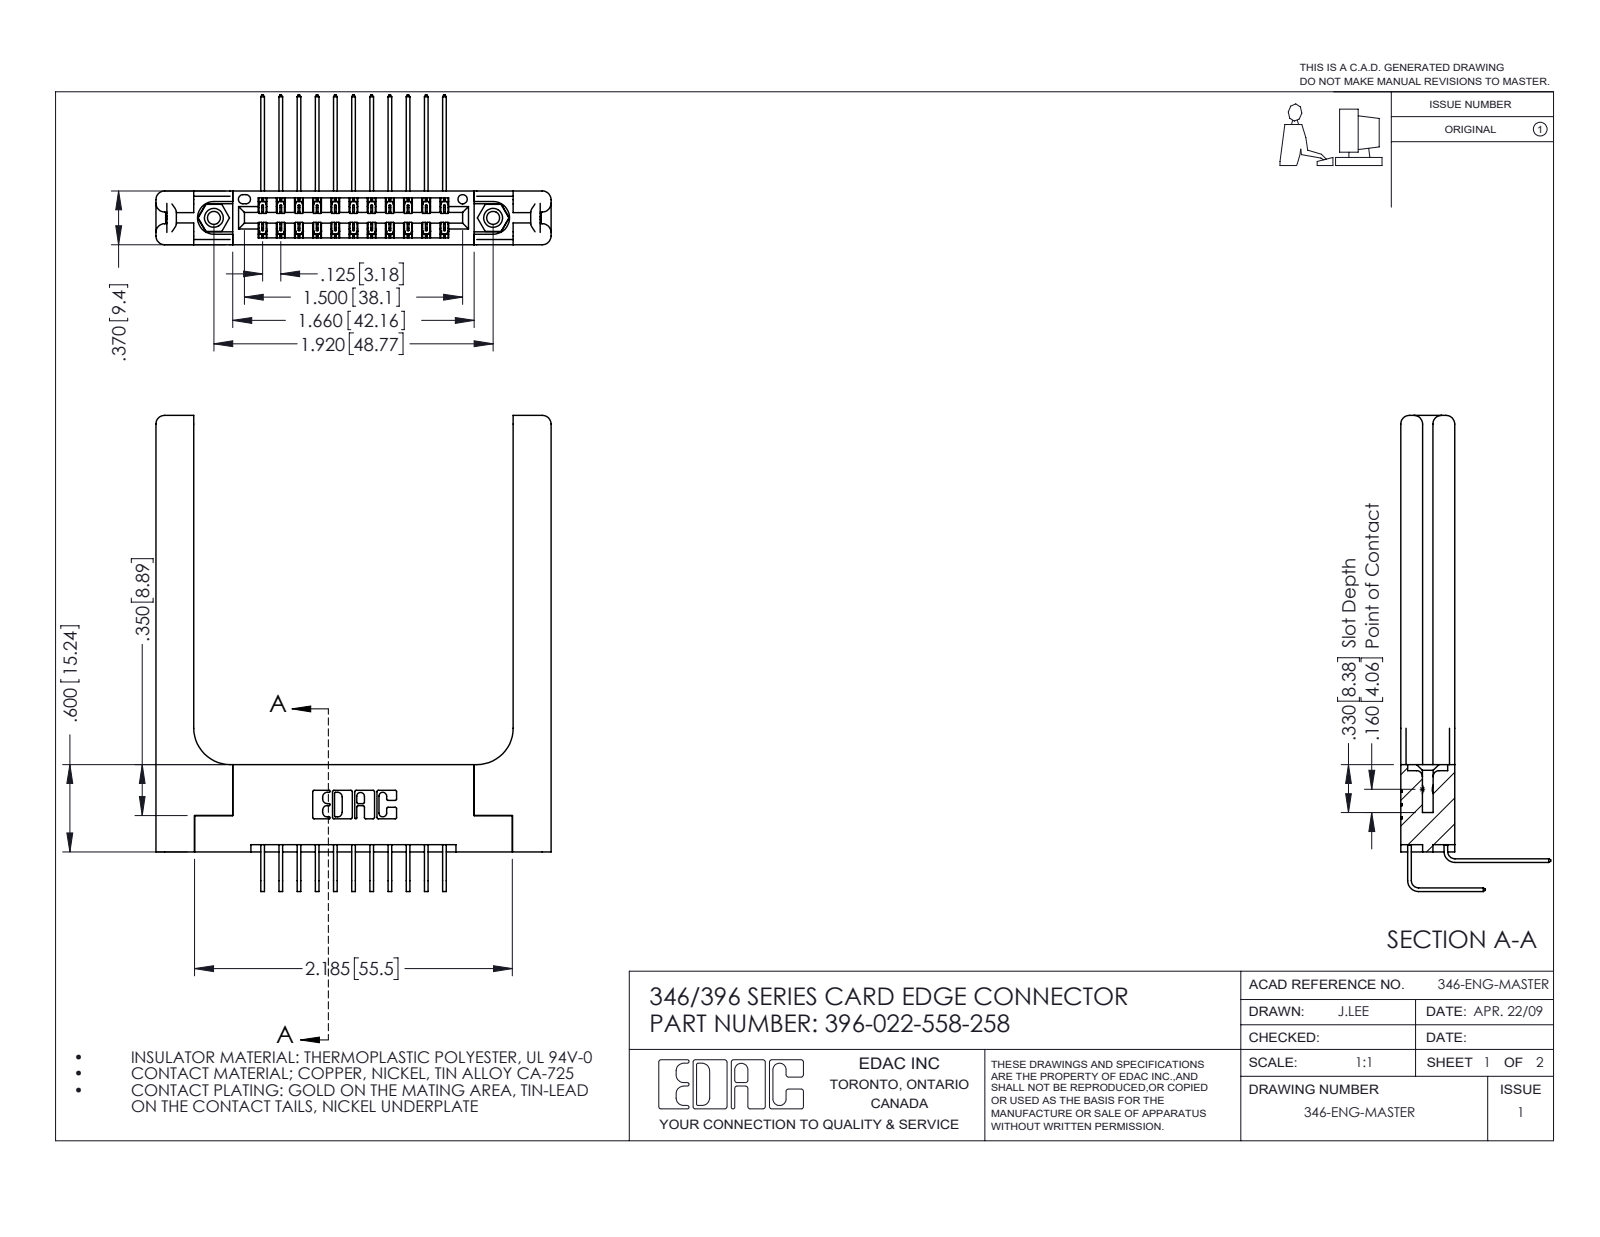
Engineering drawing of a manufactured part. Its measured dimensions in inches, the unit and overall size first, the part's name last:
Units: inches
Overall size (bounding box): 3.273 × 2.716 × 1.03
Round holes (diameter × count): ⌀0.089 ×2, ⌀0.125 ×2, ⌀0.156 ×2, ⌀0.064 ×1
Round bosses / shafts (diameter × count): ⌀0.155 ×2
Partial cylindrical surfaces — rounded edges, fillets, slot ends (radius × count): R0.006 ×33, R0.01 ×22, R0.06 ×16, R0.007 ×6, R0.031 ×6, R0.026 ×3, R0.014 ×2, R0.022 ×2
Main face-to-face distances: 0.37, 0.15, 0.072, 0.322, 0.048, 0.148, 0.22, 0.102, 0.25, 0.173
Hole centre spacings: 0.246, 1.715, 1.92
Volume: 0.861 in³ · Surface area: 21.99 in²
Bodies: 27 solids, 1566 faces (1038 planar, 468 cylindrical, 60 other)
Part name (STEP PRODUCT): 346-220-058_345-220-058; 345-292-001_558 559 Tail - 1; 396-022-558-258; 345-250-001_345-250-001-102 (+2 more)
STEP written by: SolidWorks 2016 (CONFIG_CONTROL_DESIGN)
